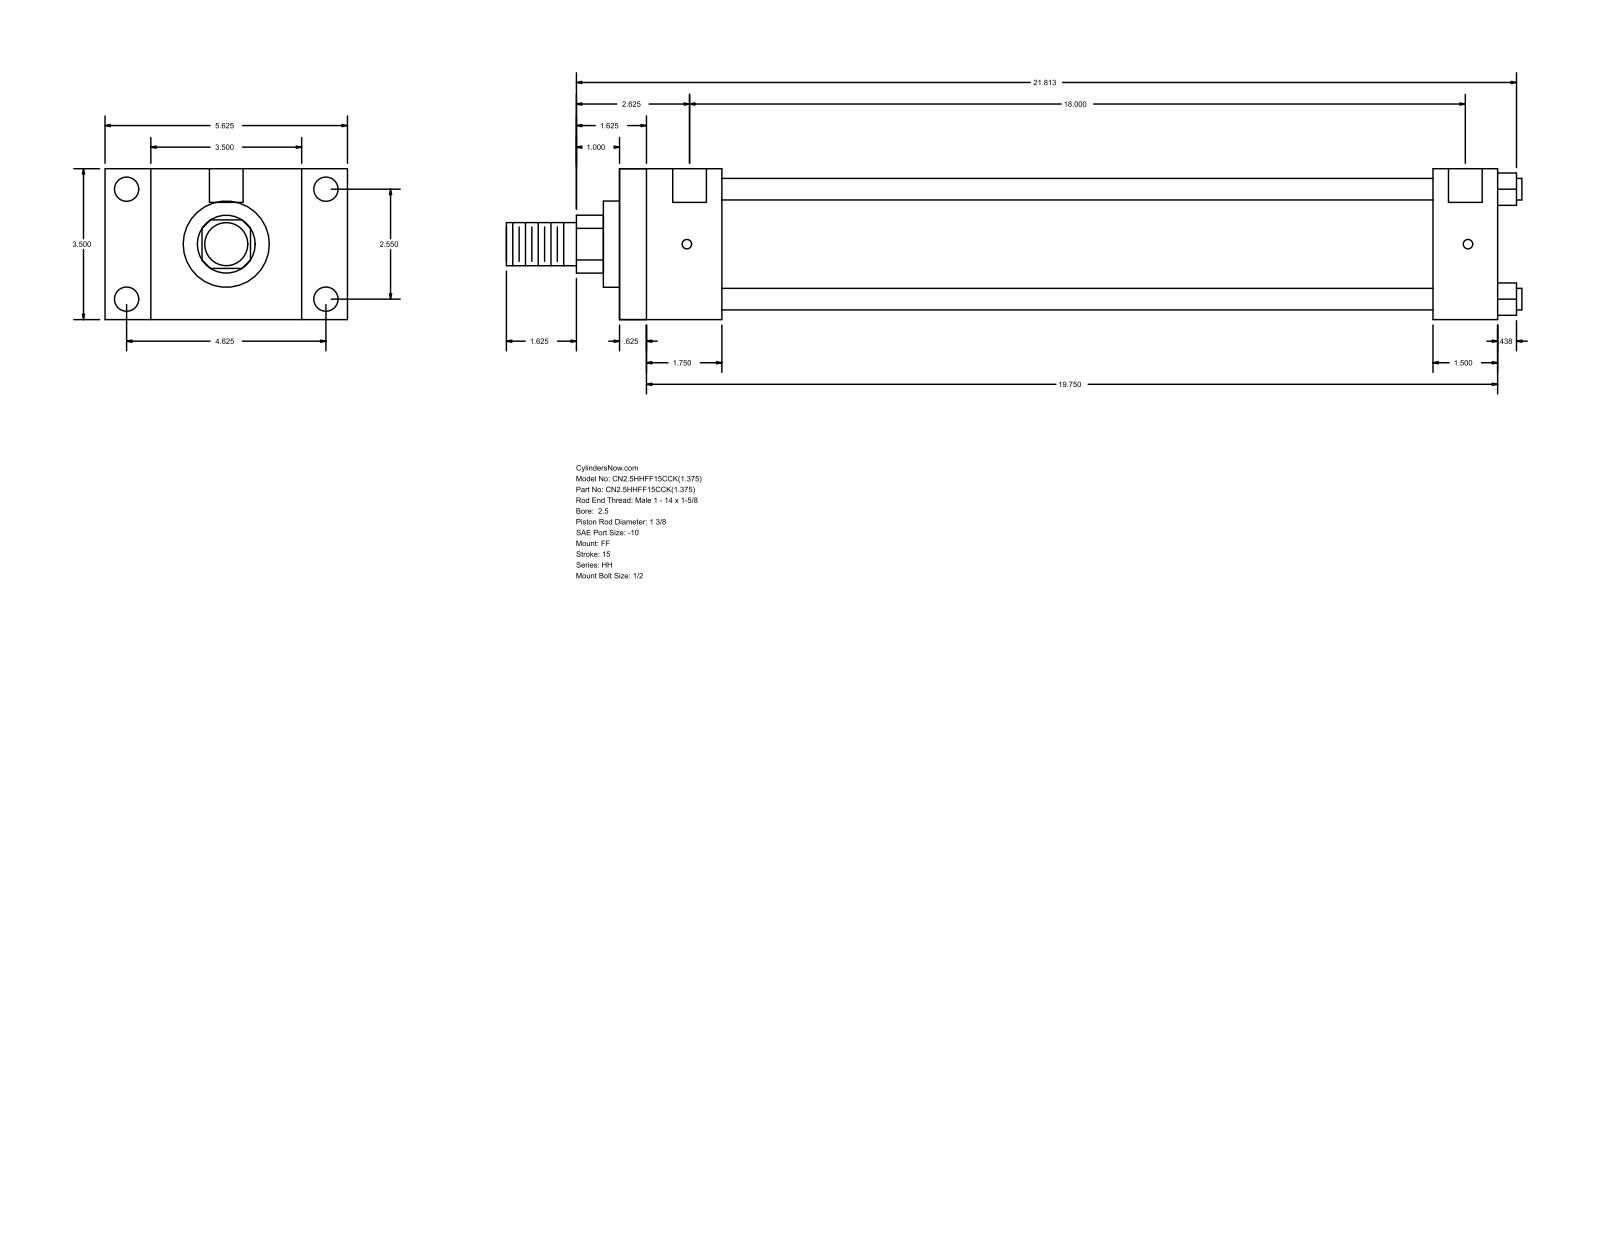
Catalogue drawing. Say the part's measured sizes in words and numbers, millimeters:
The part is named "HH_FF__0250_1.375". Its 3-D file was written by "GSSL Pune (CONFIG_CONTROL_DESIGN)". It is 0 solids with 92 faces: 64 planar, 28 cylindrical and 0 other. Overall it measures 598.49 by 142.88 by 88.9 millimeters. Round holes: 4 of diameter 5.56, 4 of diameter 14.3, 2 of diameter 19.84. Round bosses or shafts: 4 of diameter 12.7, 1 of diameter 73.03, 1 of diameter 50.8, 1 of diameter 34.92, 1 of diameter 25.4. Partial cylindrical surfaces (rounded edges, fillets, slot ends): 1 of radius 17.06. The main face-to-face distances are 88.9, 517.52, 15.87, 501.65, 60.32, 44.45, 457.2, 479.42, 463.55, 419.1. The hole center spacings are 1.58, 64.76, 117.48, 134.15, 458.79, 460.37, 457.21.
